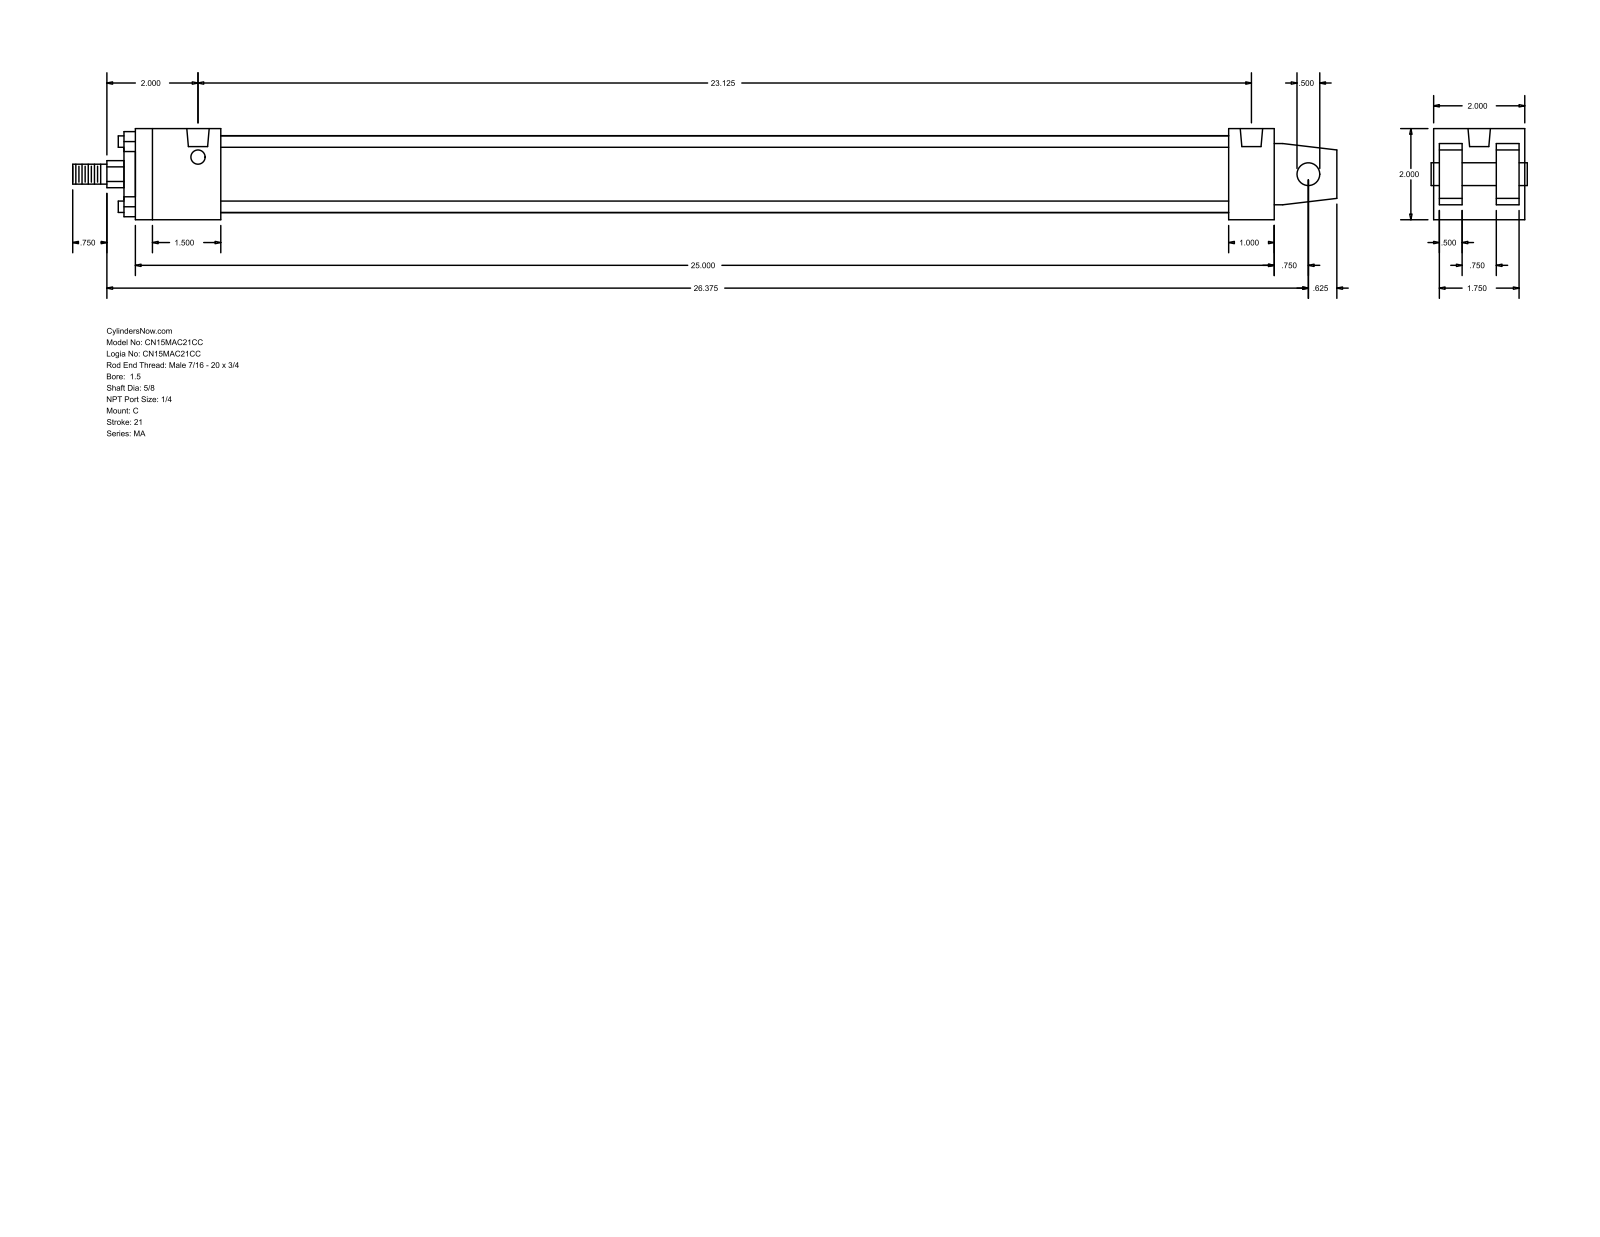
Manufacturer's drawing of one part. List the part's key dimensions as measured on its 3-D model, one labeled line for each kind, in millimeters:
Part name (STEP PRODUCT): MA_C__0150_0.625
STEP written by: GSSL Pune (CONFIG_CONTROL_DESIGN)
Units: millimetres
Bodies: 0 solids, 103 faces (76 planar, 27 cylindrical, 0 other)
Overall size (bounding box): 704.85 × 50.8 × 50.8
Round holes (diameter × count): ⌀7.94 ×4, ⌀12.49 ×2
Round bosses / shafts (diameter × count): ⌀6.35 ×4, ⌀42.93 ×1, ⌀28.57 ×1, ⌀15.88 ×1, ⌀12.7 ×1, ⌀11.11 ×1
Partial cylindrical surfaces — rounded edges, fillets, slot ends (radius × count): R7.54 ×1
Main face-to-face distances: 50.8, 12.7, 34.93, 15.87, 3.17, 47.63, 31.76, 635, 25.4, 609.6
Hole centre spacings: 587.37
